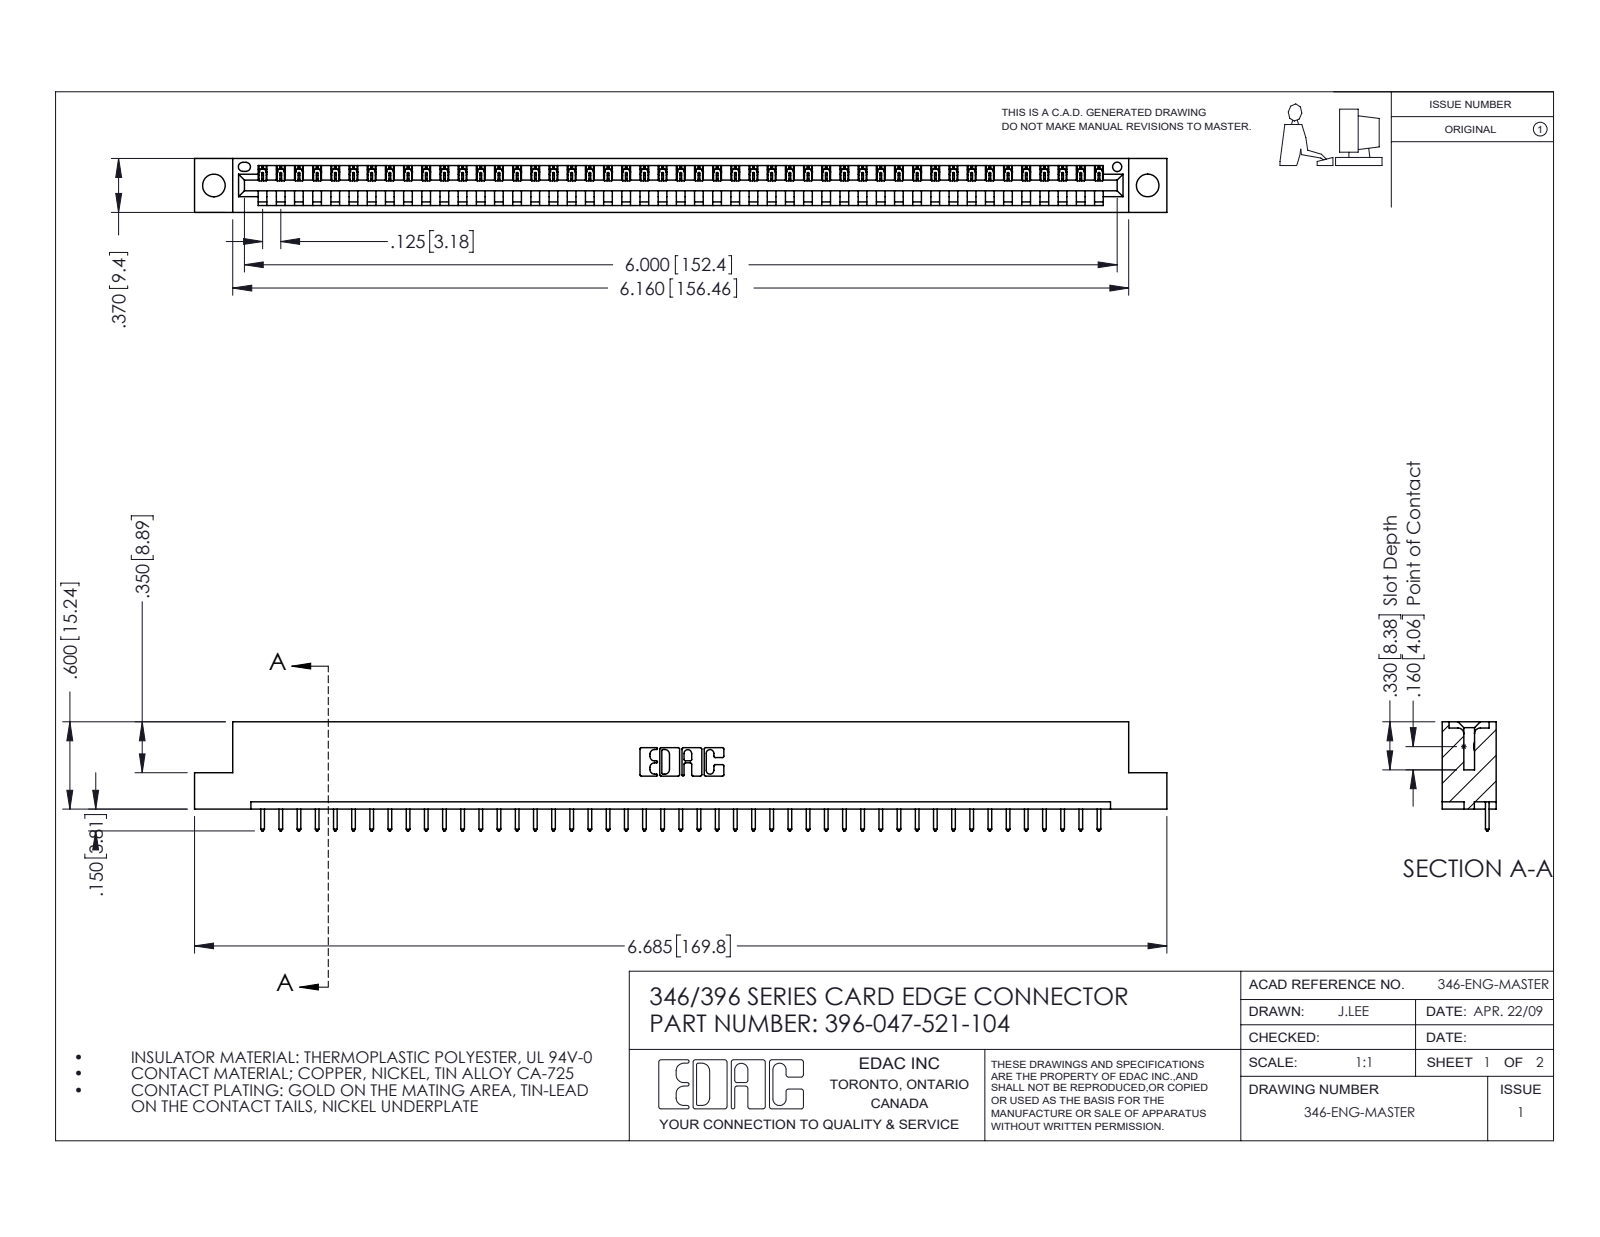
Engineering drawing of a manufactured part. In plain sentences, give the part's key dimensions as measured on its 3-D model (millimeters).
The part is named "396-047-521-104; 346 Part_Flush Mounting Lugs - 0.156 Dia-TH; 345-292-001_345-293-121". Its 3-D file was written by "SolidWorks 2016 (CONFIG_CONTROL_DESIGN)". It is 48 solids with 2848 faces: 1956 planar, 892 cylindrical and 0 other. Overall it measures 169.8 by 19.1 by 9.4 millimeters. Its volume is 16 100 cubic millimeters and its surface area 19 410 square millimeters. Round holes: 2 of diameter 4, 1 of diameter 1.6. Partial cylindrical surfaces (rounded edges, fillets, slot ends): 94 of radius 0.2, 94 of radius 0.3, 22 of radius 0.3, 6 of radius 0.2, 6 of radius 0.8, 3 of radius 0.7, 2 of radius 0.8, 2 of radius 1. The main face-to-face distances are 1.2, 8.2, 9.4, 6.4, 1.8, 7.6, 0.6, 3.8, 5.6, 2.5. The hole center spacings are 6.2, 157.8, 163.1.
